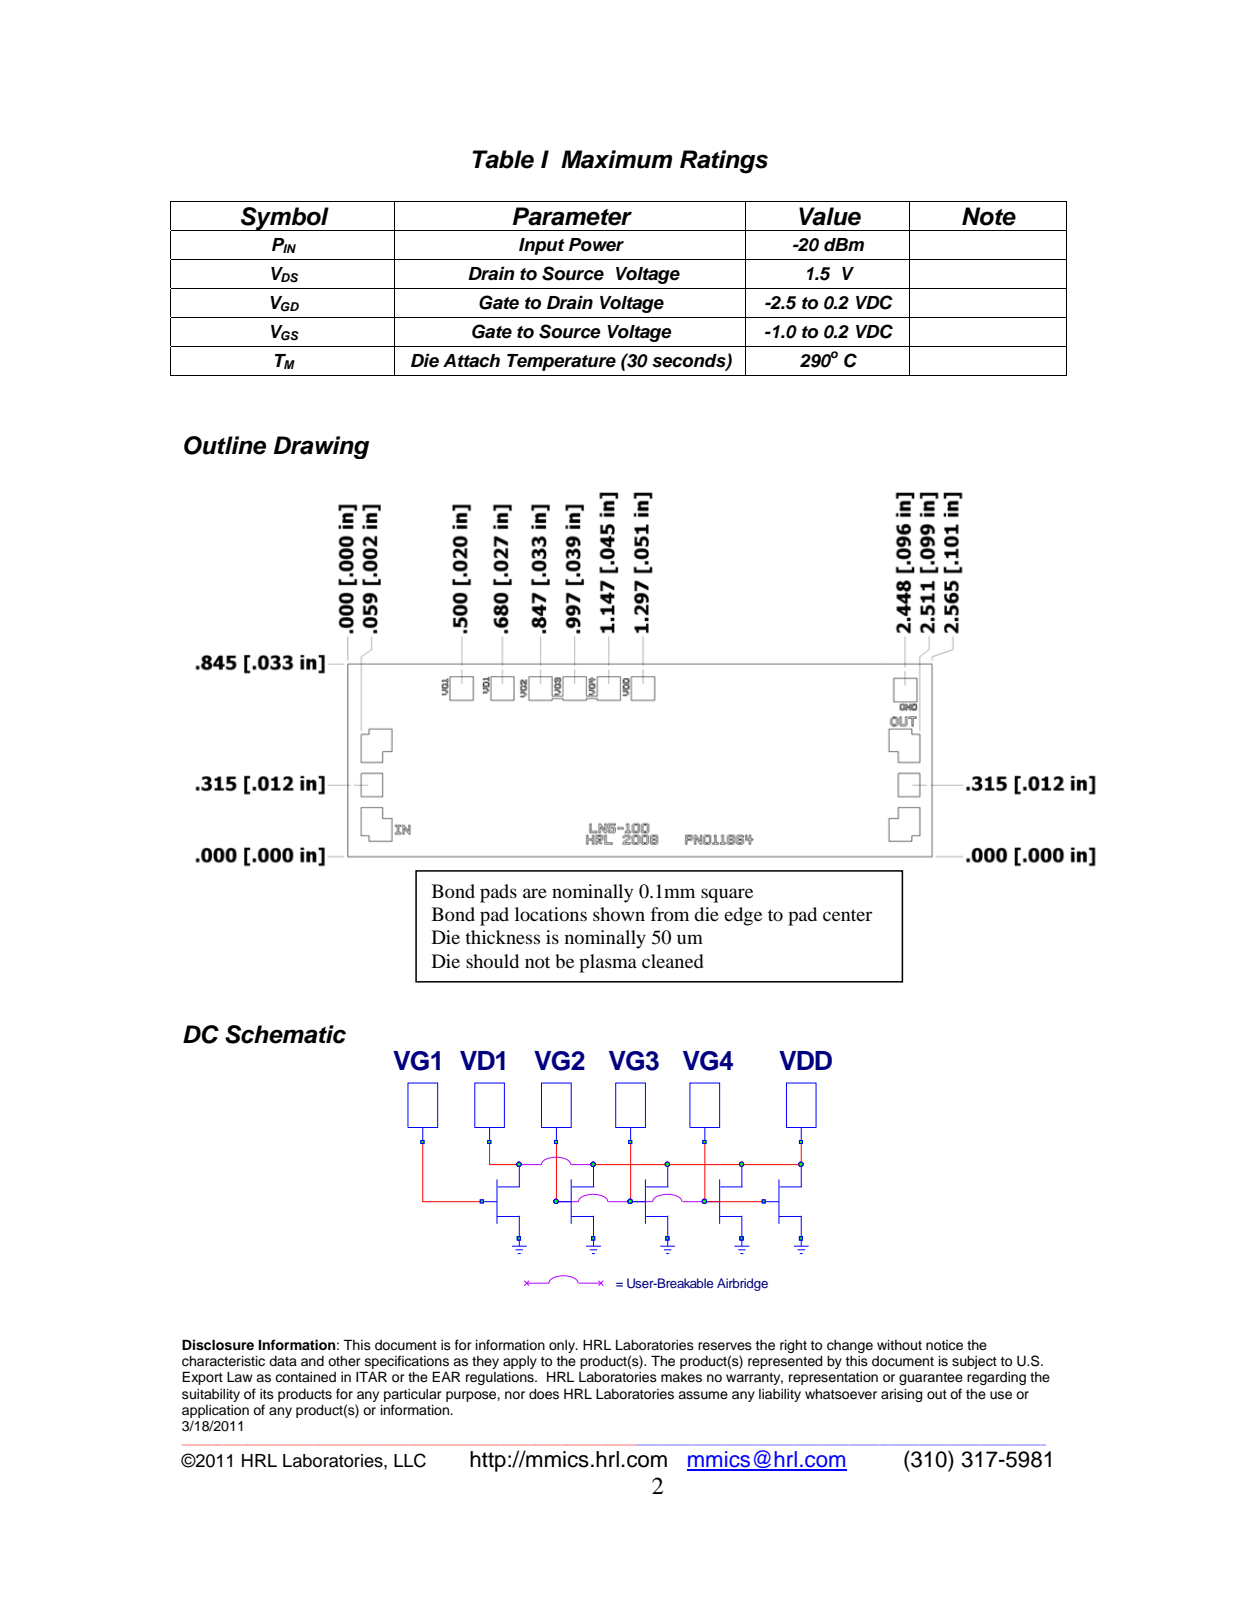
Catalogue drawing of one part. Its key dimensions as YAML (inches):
part_name: "LN5-100"
step_written_by: "Autodesk Inventor 2009 (AUTOMOTIVE_DESIGN)"
units: inches
bodies: {solids: 2, faces: 1030, planar: 1030, cylindrical: 0, other: 0}
overall_size: [0.101, 0.033, 0.002]
face_to_face_distances: [0.033, 0.101, 0.026, 0.024, 0.024, 0.027, 0.024, 0.018, 0.025, 0.022]
